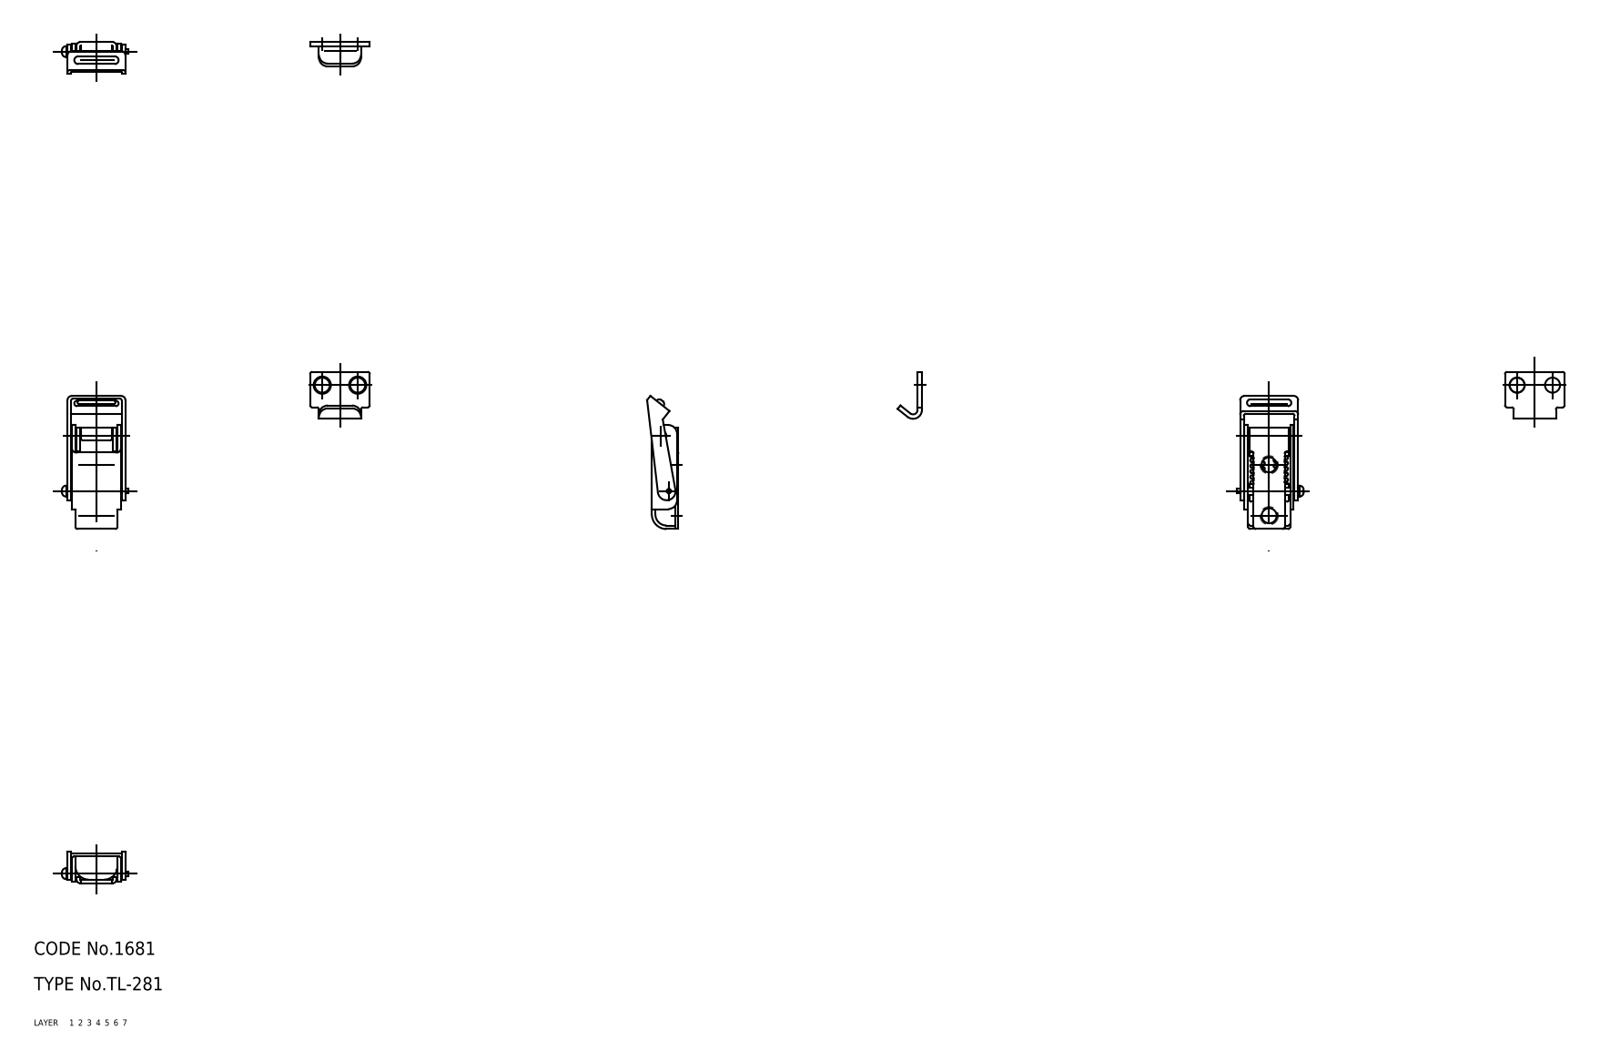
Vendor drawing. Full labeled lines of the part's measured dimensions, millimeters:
Part name (STEP PRODUCT): 67122910; 67122923; 67122936; 67122949 (+5 more)
STEP written by: CADfix (AUTOMOTIVE_DESIGN)
Units: millimetres
Bodies: 9 solids, 229 faces (0 planar, 0 cylindrical, 229 other)
Overall size (bounding box): 35.5 × 15 × 7.07
Volume: 991 mm³ · Surface area: 2 997 mm²
